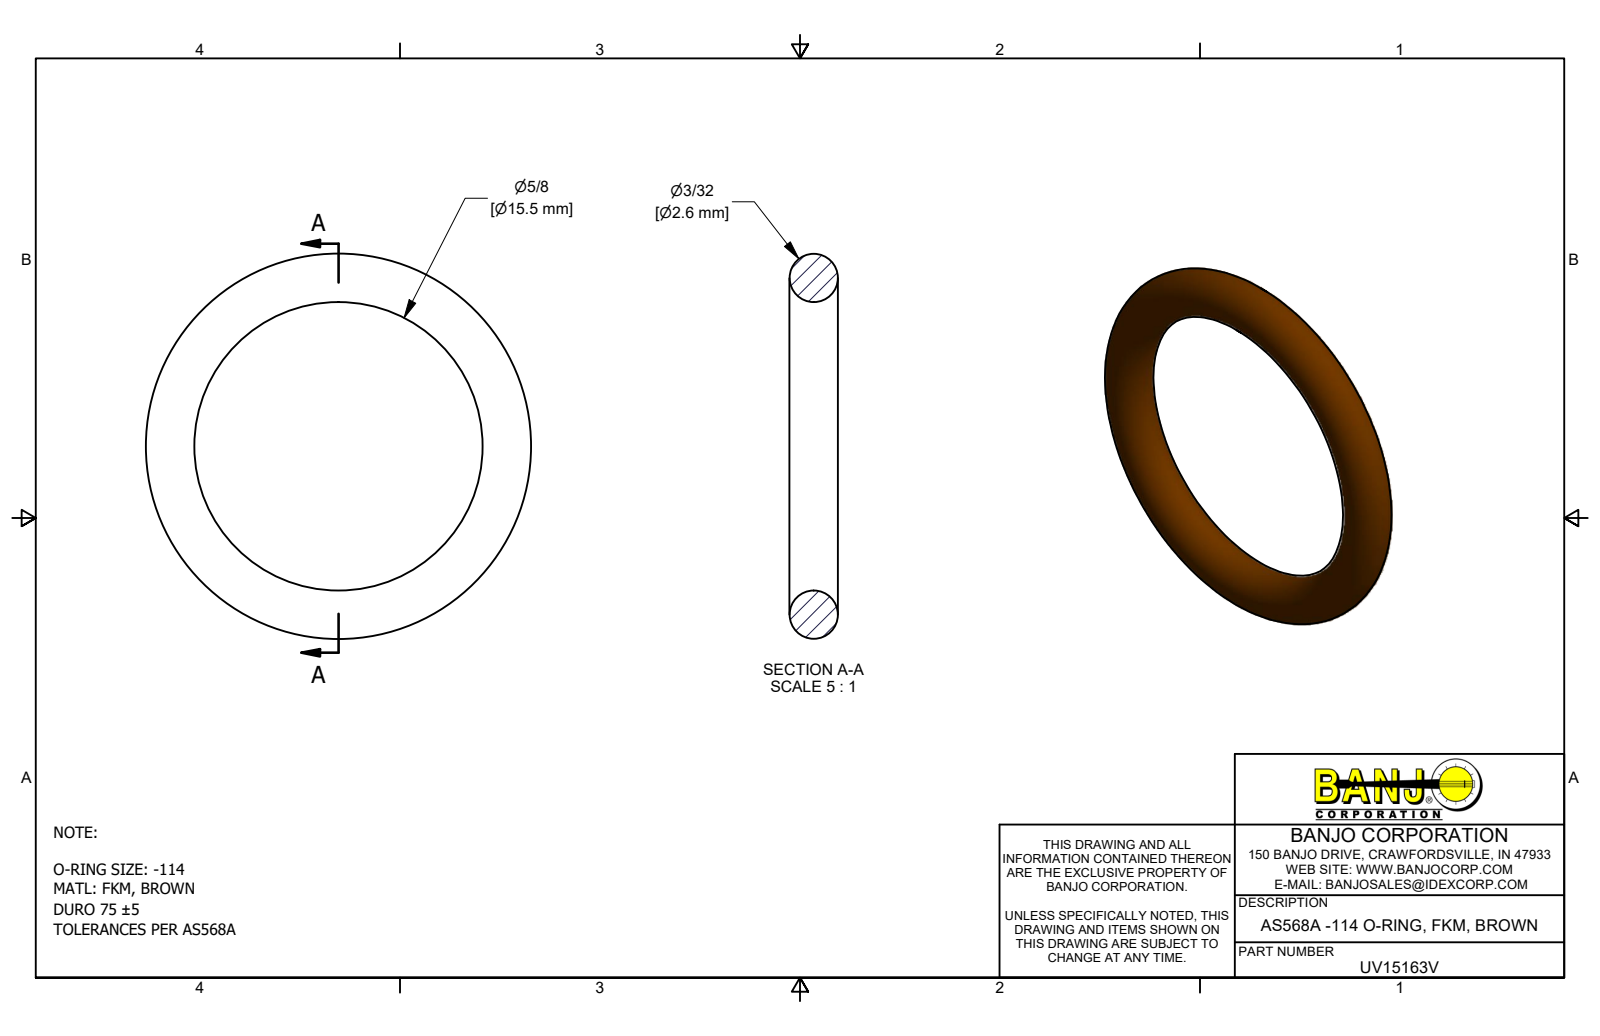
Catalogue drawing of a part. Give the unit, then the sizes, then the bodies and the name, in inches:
Units: inches
Overall size (bounding box): 0.818 × 0.818 × 0.103
Volume: 0.019 in³ · Surface area: 0.727 in²
Bodies: 1 solid, 1 faces (0 planar, 0 cylindrical, 1 other)
Part name (STEP PRODUCT): UV15163V
STEP written by: Autodesk Inventor 2019 (AUTOMOTIVE_DESIGN)
